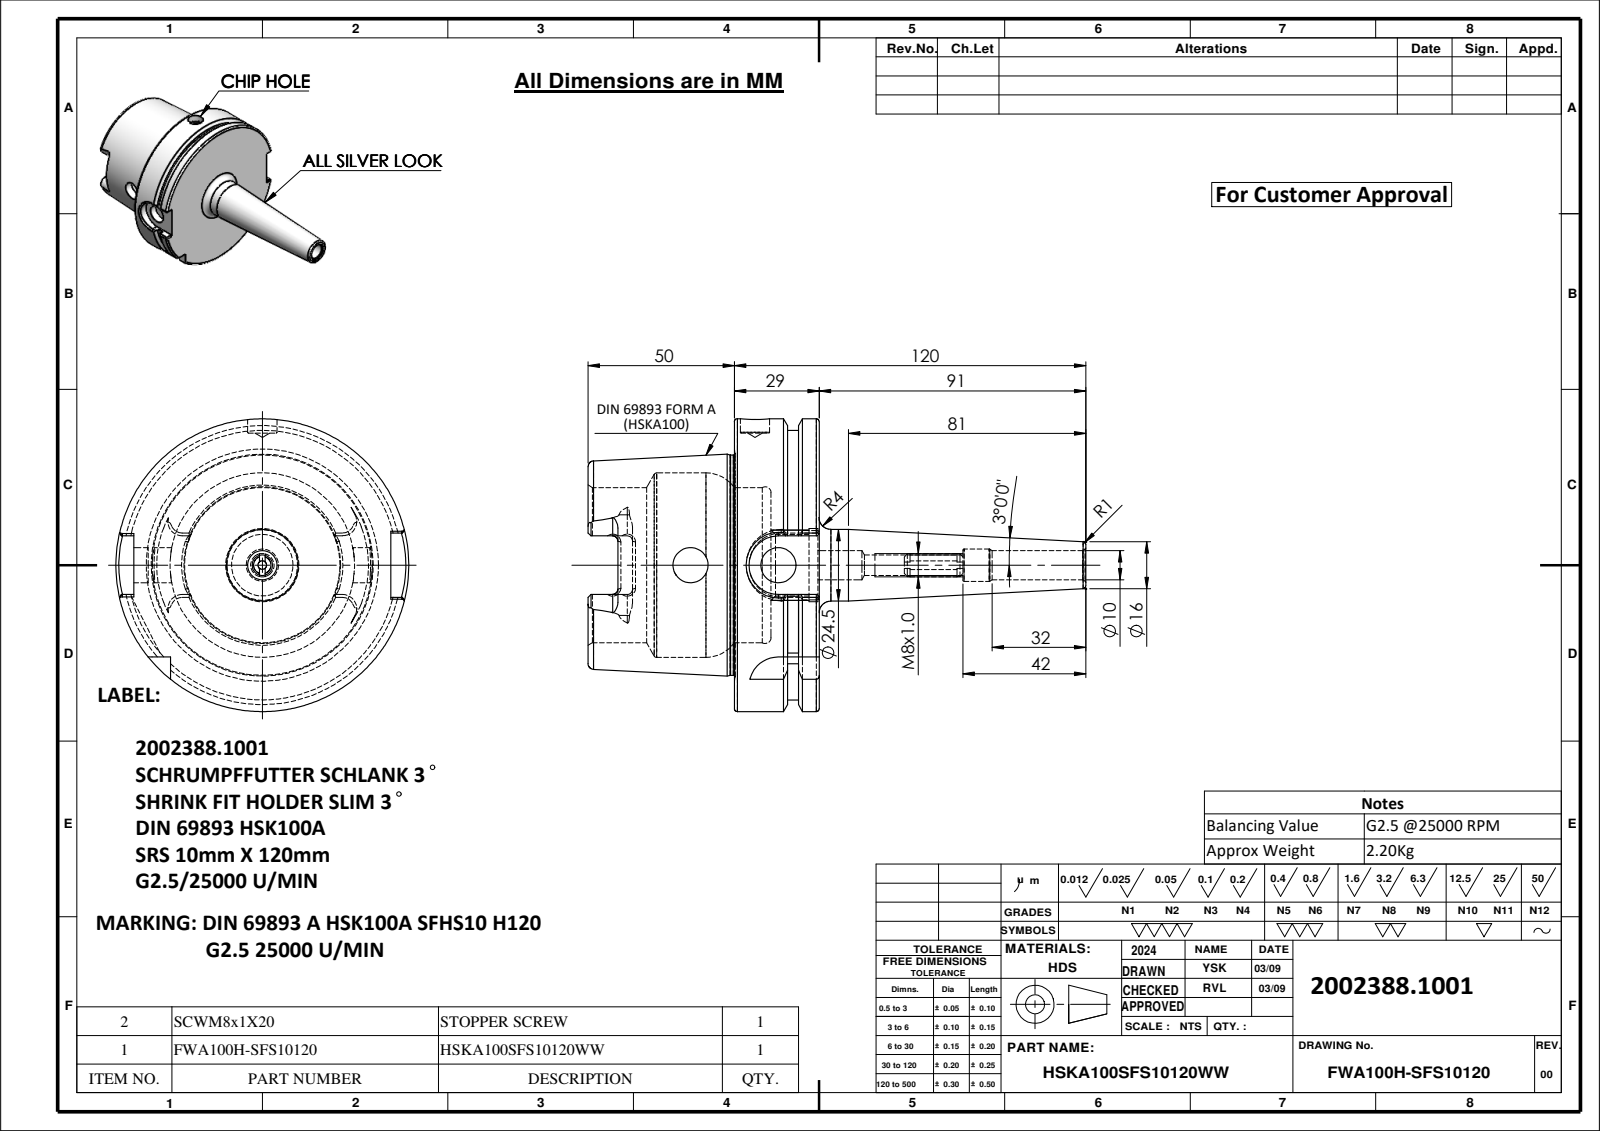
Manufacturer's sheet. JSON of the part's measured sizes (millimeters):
{"part_name": "FWA100H-SFS10120; HSKA100SFS10120WW; SCWM8X1", "step_written_by": "SolidWorks 2024 (CONFIG_CONTROL_DESIGN)", "units": "millimeters", "bodies": {"solids": 2, "faces": 210, "planar": 68, "cylindrical": 58, "other": 84}, "overall_size": [170, 100, 100], "volume_mm3": 279941, "surface_area_mm2": 58657, "round_holes": [[10, 2], [12, 2], [3, 1], [7, 1], [11, 1], [21, 1], [25, 1], [53, 1], [63, 1]], "round_bosses_or_shafts": [[100, 1], [92, 1], [75.16, 1], [24.5, 1], [8, 1]], "partial_cylinders_radius": [[1.8, 6], [4.88, 4], [10, 2], [11, 1]], "face_to_face_distances": [28.95, 12.5, 16.45, 50, 62.5, 78.95, 16, 78.5, 28.5, 0.45], "hole_center_spacings": [30]}
